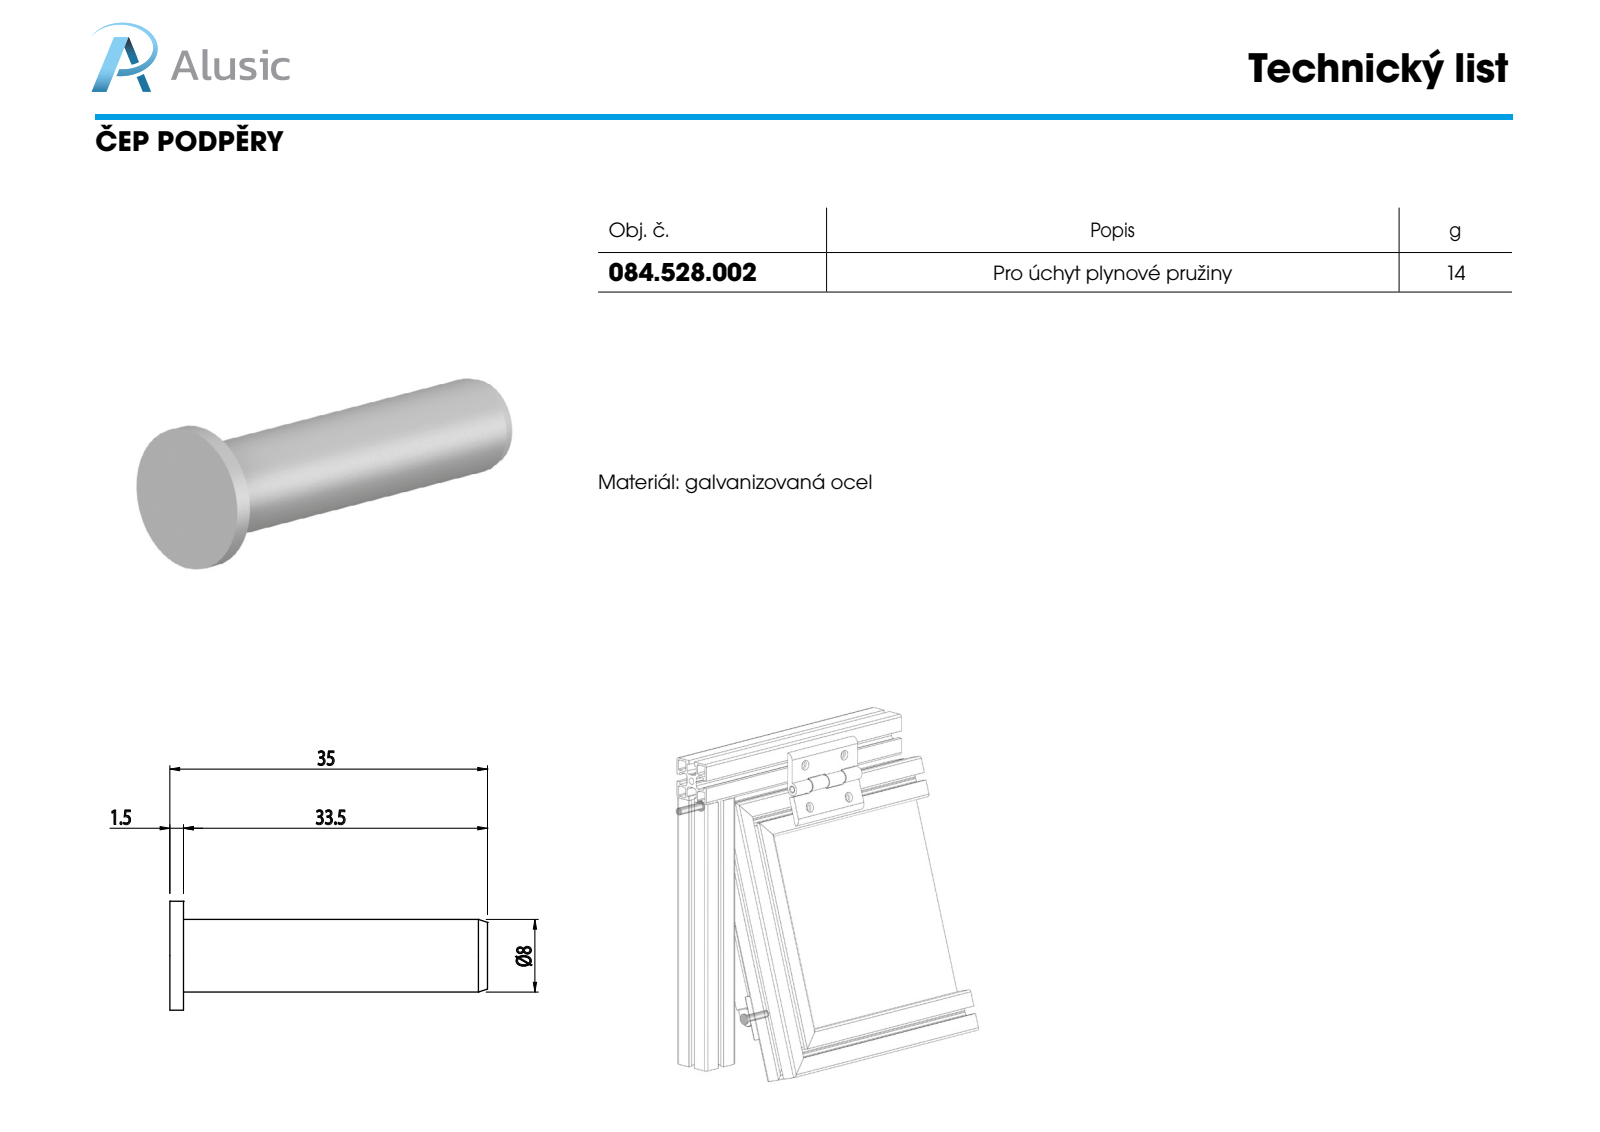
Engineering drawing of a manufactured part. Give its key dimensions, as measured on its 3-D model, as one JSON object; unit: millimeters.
{"part_name": "084.528.002", "step_written_by": "SolidWorks 2011 (CONFIG_CONTROL_DESIGN)", "units": "millimeters", "bodies": {"solids": 1, "faces": 9, "planar": 3, "cylindrical": 4, "other": 2}, "overall_size": [35, 12, 12], "volume_mm3": 1850, "surface_area_mm2": 1117, "round_bosses_or_shafts": [[12, 1], [8, 1]], "face_to_face_distances": [1.5, 35, 33.5]}
